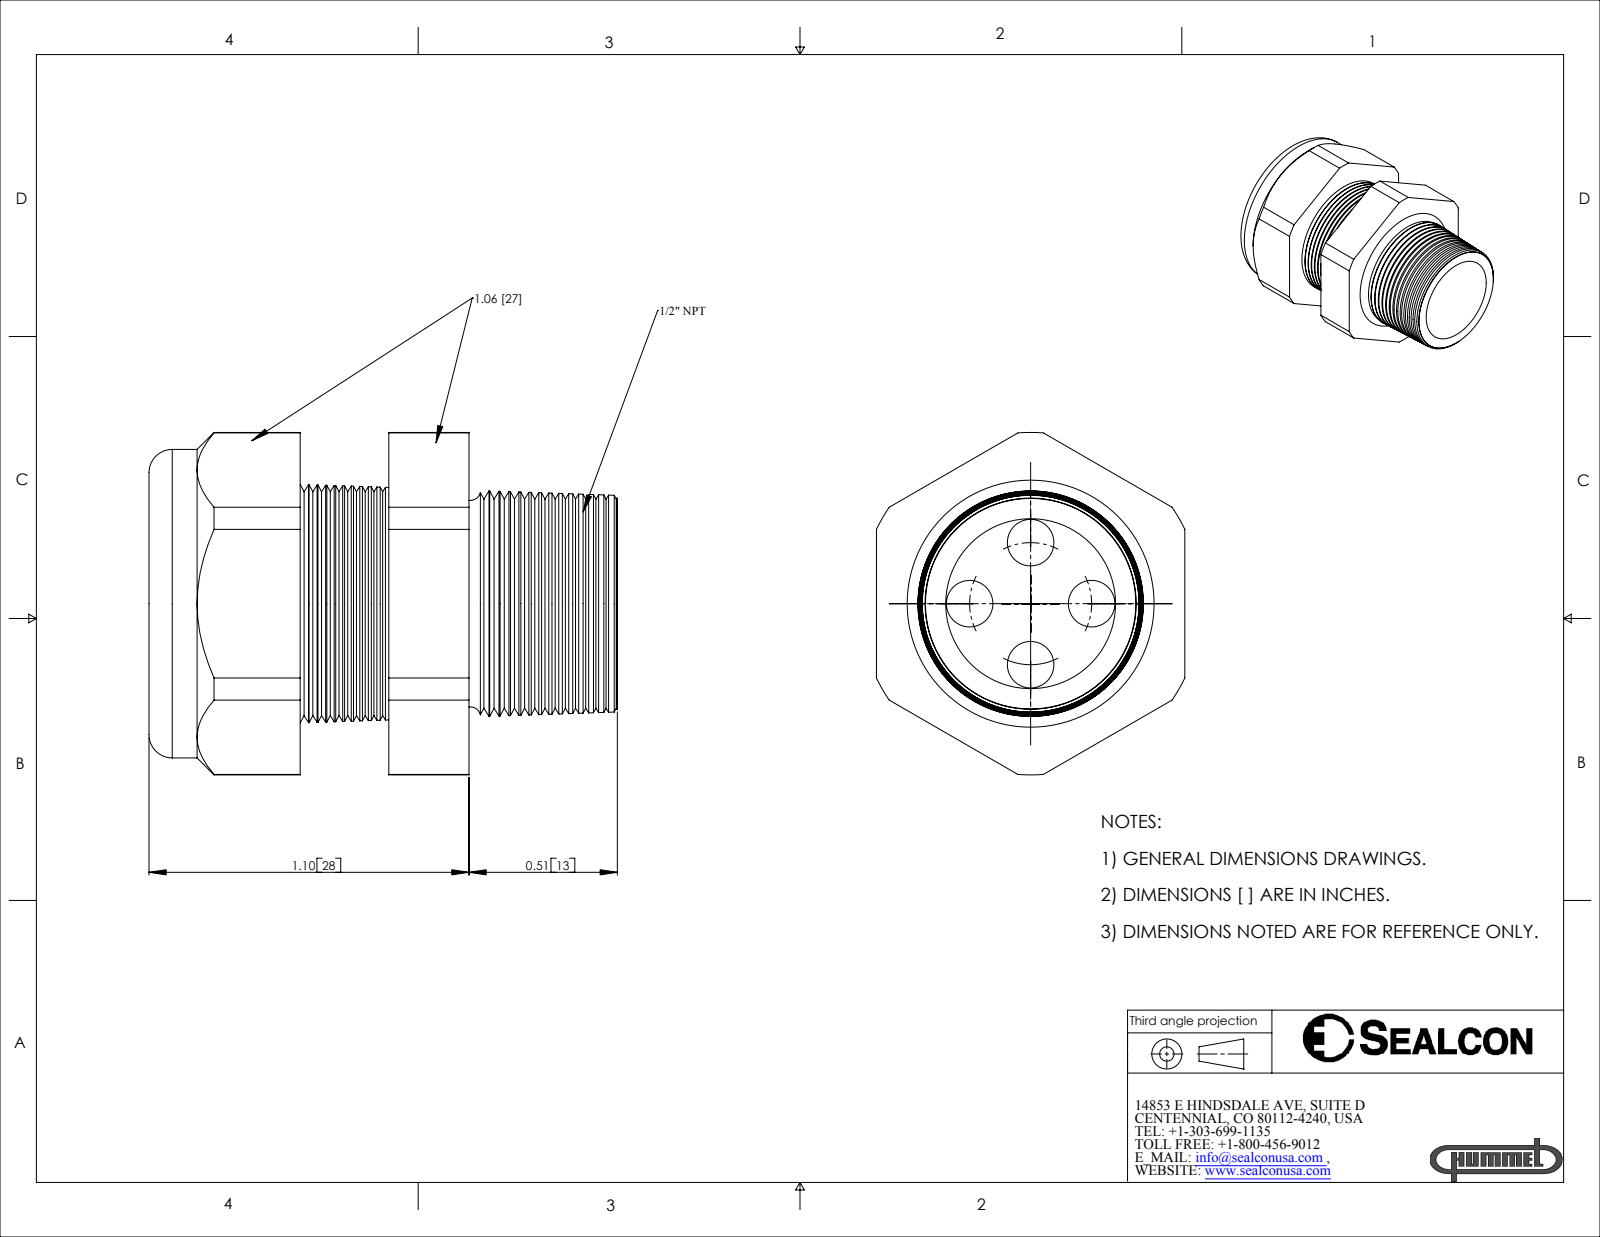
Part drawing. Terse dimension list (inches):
name: CD16N3-GY
written by: SolidWorks 2007 (CONFIG_CONTROL_DESIGN)
unit: in
bodies: 2 solids, 206 faces (20 planar, 28 cylindrical, 158 other)
size: 1.61 × 1.177 × 1.06
volume: 0.737 in³; area: 13.12 in²
holes: 4× ⌀0.16, 1× ⌀0.58, 1× ⌀0.6
bosses: 1× ⌀1.06
rounds: 1× R0.588
face distances: 1.06, 0.305, 0.58, 0.276, 0.52, 0.824, 1.1, 0.35, 0.17, 0.474
hole spacings: 0.21, 0.297, 0.42
